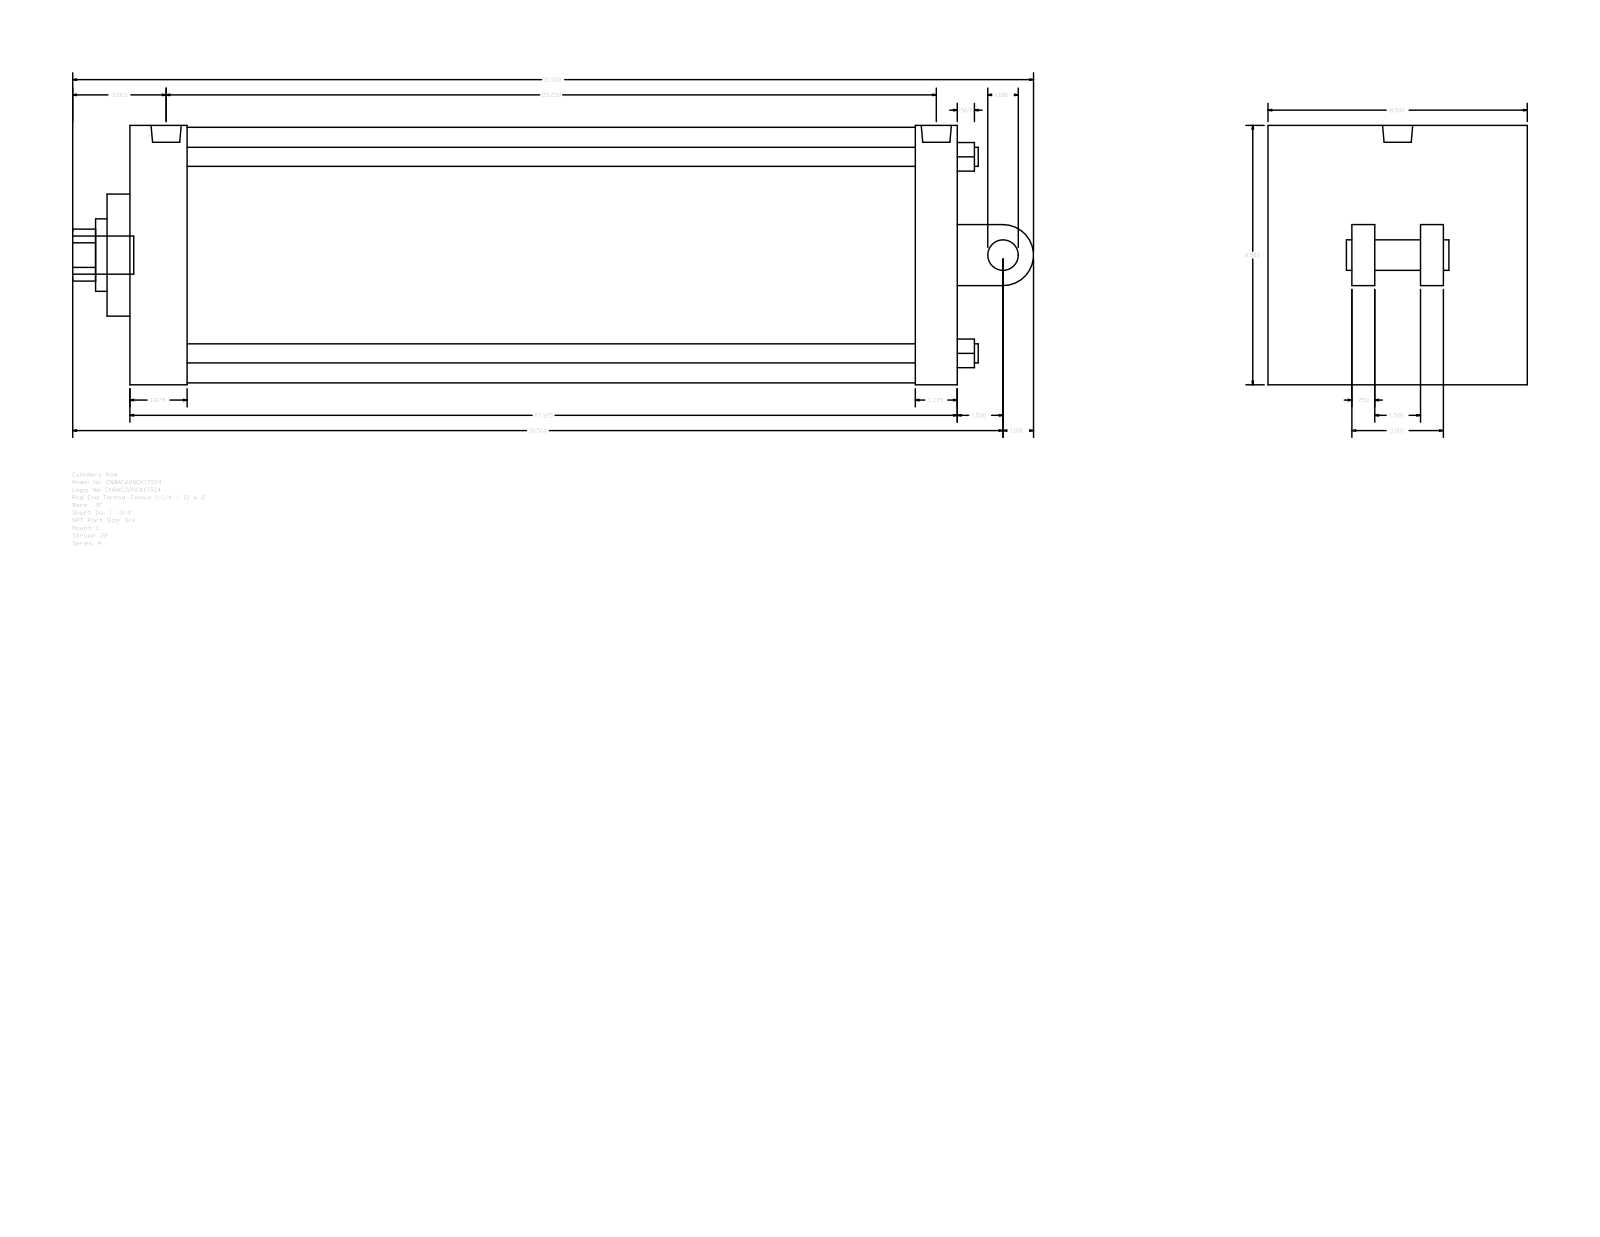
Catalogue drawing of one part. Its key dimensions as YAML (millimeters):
part_name: "A_C__0800_1.75"
step_written_by: "GSSL Pune (CONFIG_CONTROL_DESIGN)"
units: millimeters
bodies: {solids: 0, faces: 104, planar: 75, cylindrical: 29, other: 0}
overall_size: [800.1, 215.9, 215.9]
round_holes:
  - {diameter: 15.88, count: 4}
  - {diameter: 15.08, count: 2}
  - {diameter: 25.12, count: 1}
  - {diameter: 44.45, count: 1}
  - {diameter: 60.33, count: 1}
  - {diameter: 212.72, count: 1}
round_bosses_or_shafts:
  - {diameter: 15.08, count: 2}
  - {diameter: 31.75, count: 1}
  - {diameter: 25.4, count: 1}
  - {diameter: 25.12, count: 1}
partial_cylinders:
  - {radius: 21.63, count: 1}
  - {radius: 25.4, count: 1}
face_to_face_distances: [688.98, 215.9, 19.05, 57.15, 47.63, 641.35, 654.05, 606.42, 34.93, 88.9]
hole_center_spacings: [115.67, 163.58, 231.34, 6.35]
